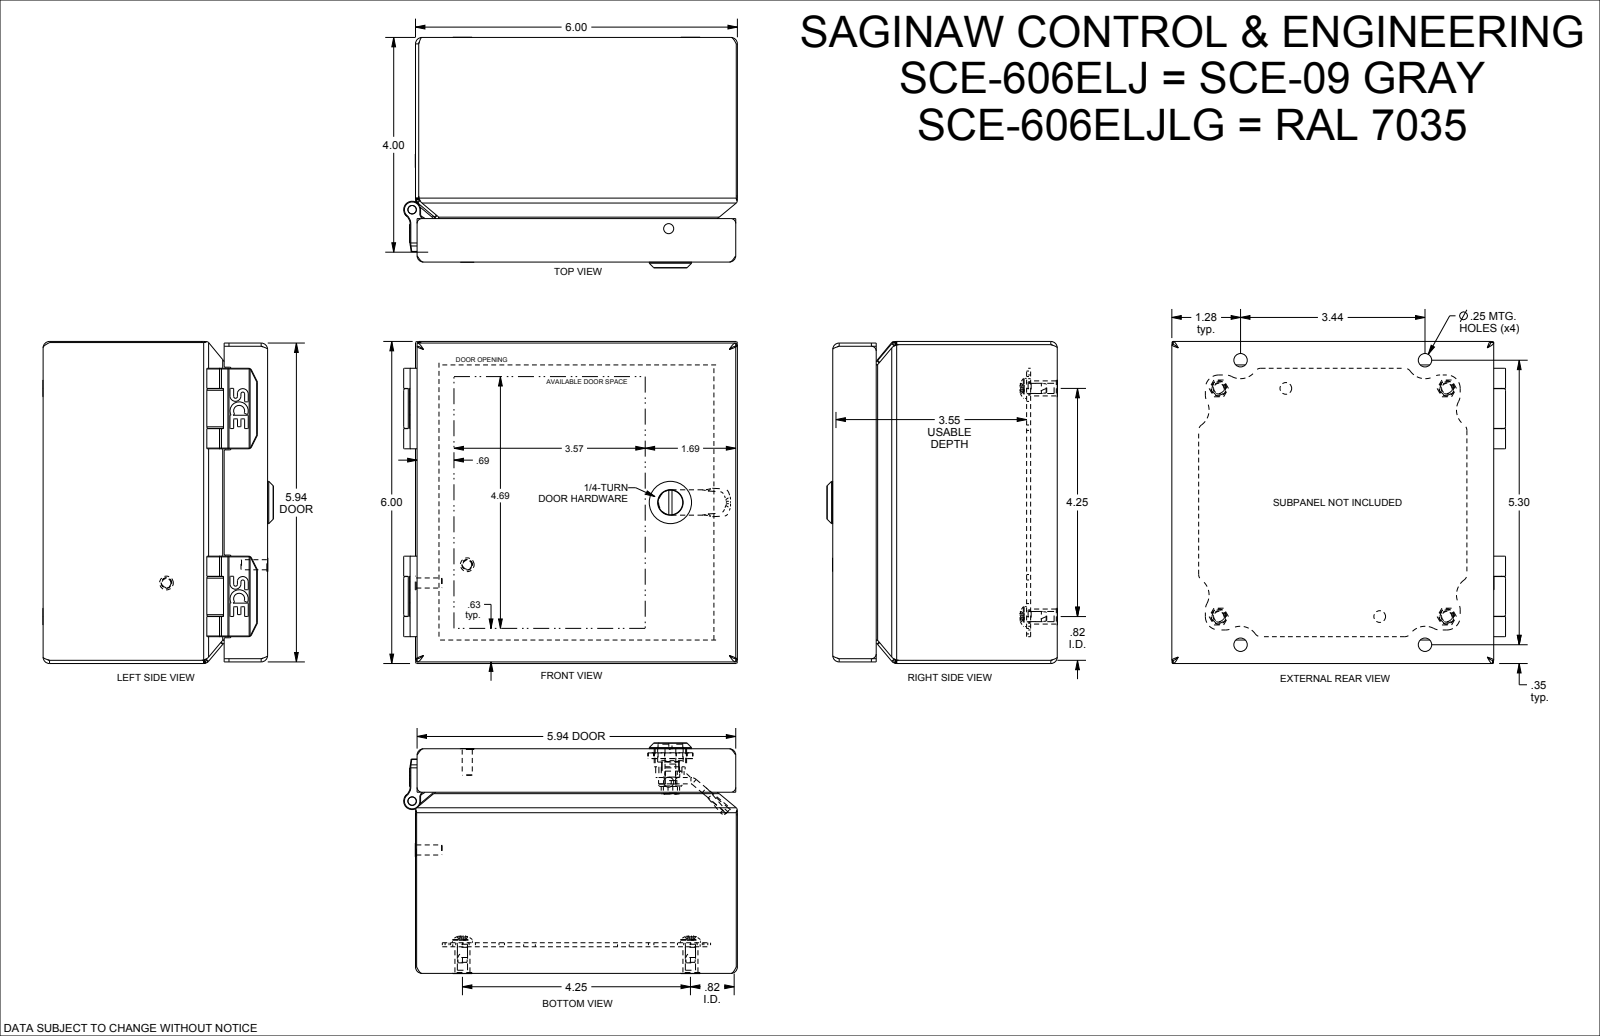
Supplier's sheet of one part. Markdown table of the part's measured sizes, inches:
| quantity | value |
| --- | --- |
| part name | SCE-606ELJLG |
| STEP written by | SolidWorks 2019 (CONFIG_CONTROL_DESIGN) |
| units | inches |
| bodies | 0 solids, 2654 faces (858 planar, 764 cylindrical, 1032 other) |
| overall size | 6.22 × 6 × 4.296 |
| round holes (diameter × count) | 0.25 × 8, 0.19 × 4, 0.284 × 4, 0.479 × 4, 0.02 × 2, 0.1 × 2, 0.174 × 2, 0.196 × 2, 0.218 × 2, 0.266 × 2, 0.158 × 1, 0.187 × 1 |
| round bosses / shafts (diameter × count) | 0.188 × 6, 0.373 × 4, 0.28 × 4, 0.17 × 4, 0.16 × 4, 0.135 × 4, 0.108 × 4, 0.26 × 2 |
| partial cylindrical surfaces (radius × count) | 0.106 × 132, 0.005 × 131, 0.008 × 32, 0.01 × 26, 0.025 × 24, 0.03 × 24, 0.06 × 22, 0.013 × 21 |
| main face-to-face distances | 0.06, 5.94, 0.06, 5.88, 6, 4.065, 4.124, 4.185, 4.125, 0.571 |
| hole center spacings | 0.664, 3.88, 4.25, 4.792, 6.13, 0.994, 1.25, 2.157 |
